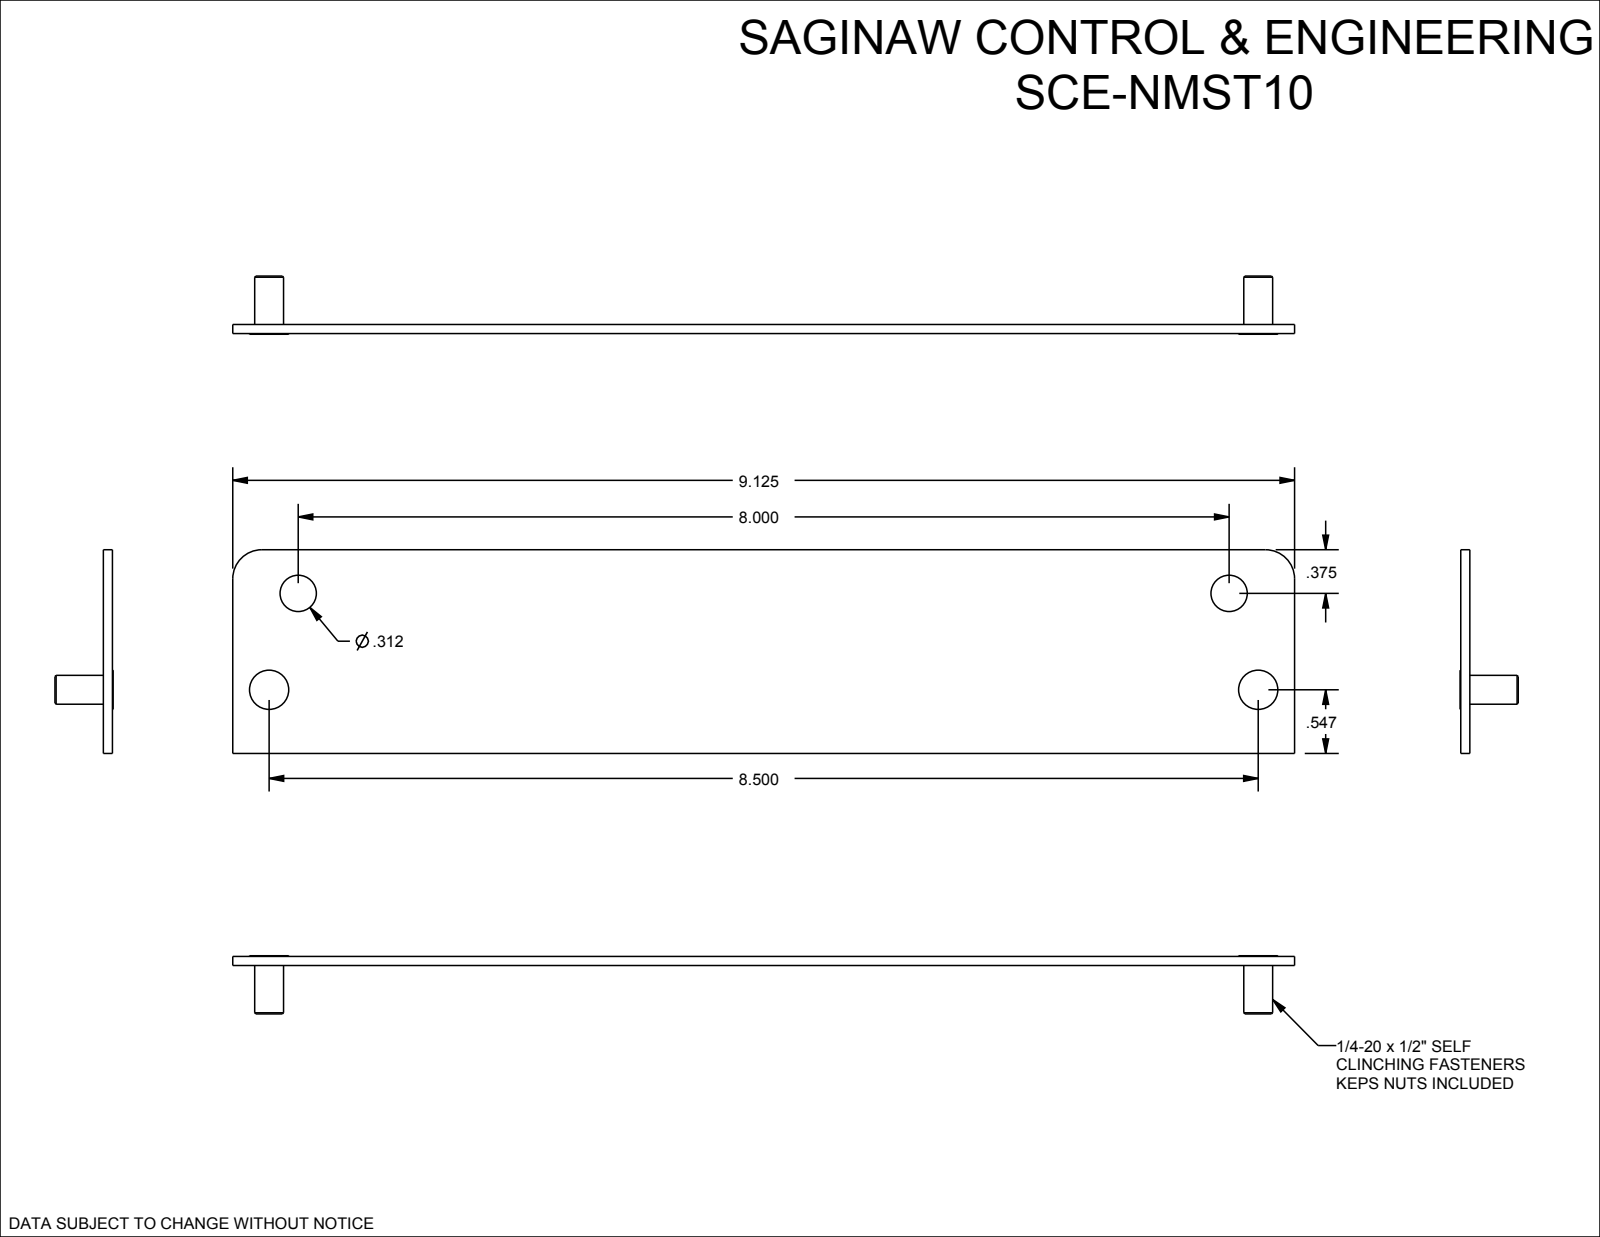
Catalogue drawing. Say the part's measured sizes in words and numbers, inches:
The part is named "SCE-NMST10". Its 3-D file was written by "SolidWorks 2019 (AUTOMOTIVE_DESIGN)". It is 3 solids with 24 faces: 12 planar, 10 cylindrical and 2 other. Overall it measures 9.125 by 1.75 by 0.5 inches. Its volume is 1.274 cubic inches and its surface area 34.47 square inches. Round holes: 2 of diameter 0.25, 2 of diameter 0.312. Round bosses or shafts: 2 of diameter 0.337, 2 of diameter 0.248. Partial cylindrical surfaces (rounded edges, fillets, slot ends): 2 of radius 0.25. The main face-to-face distances are 0.078, 1.75, 0.084, 9.125, 0.066, 0.018, 0.416, 0.482, 0.494, 0.5. The hole center spacings are 0.865, 8.291, 8, 8.5.
